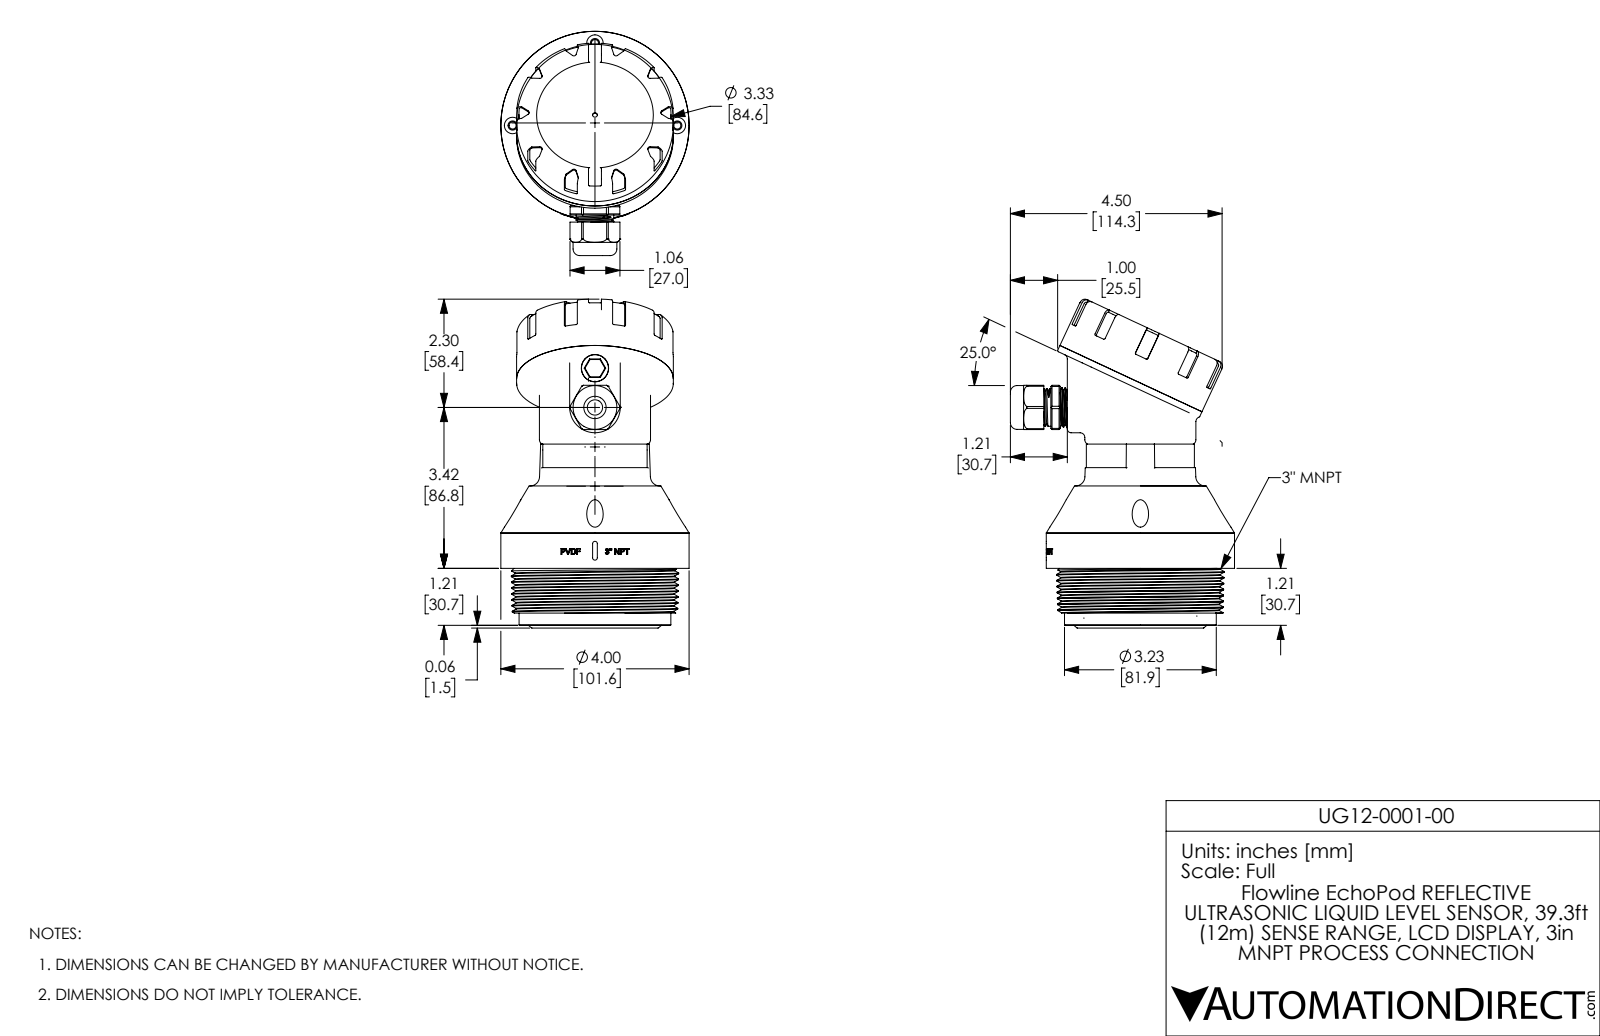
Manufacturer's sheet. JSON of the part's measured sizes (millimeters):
{"part_name": "UG12-0001-00", "step_written_by": "SolidWorks 2017 (AUTOMOTIVE_DESIGN)", "units": "millimeters", "bodies": {"solids": 9, "faces": 908, "planar": 335, "cylindrical": 230, "other": 343}, "overall_size": [177.4, 121, 101.6], "volume_mm3": 393500, "surface_area_mm2": 192500, "round_holes": [[3.8, 4], [8.9, 4], [5, 3], [2.5, 1], [5, 1], [5, 1], [8.3, 1], [12.1, 1], [13.2, 1], [20.3, 1], [21.6, 1], [23.7, 1]], "round_bosses_or_shafts": [[84.6, 2], [101.6, 1], [81.9, 1], [76.2, 1], [75.6, 1], [71.8, 1], [70.4, 1], [59.9, 1]], "partial_cylinders_radius": [[0.6, 22], [1.3, 16], [2.5, 5], [2, 2], [7.4, 1], [13.6, 1], [30.9, 1], [31.4, 1]], "face_to_face_distances": [24.1, 3.8, 2.5, 20.3, 43.2, 25.4, 19.1, 0.9, 39.4, 1.3], "hole_center_spacings": [44.5, 62.9, 88.9, 21.2]}
